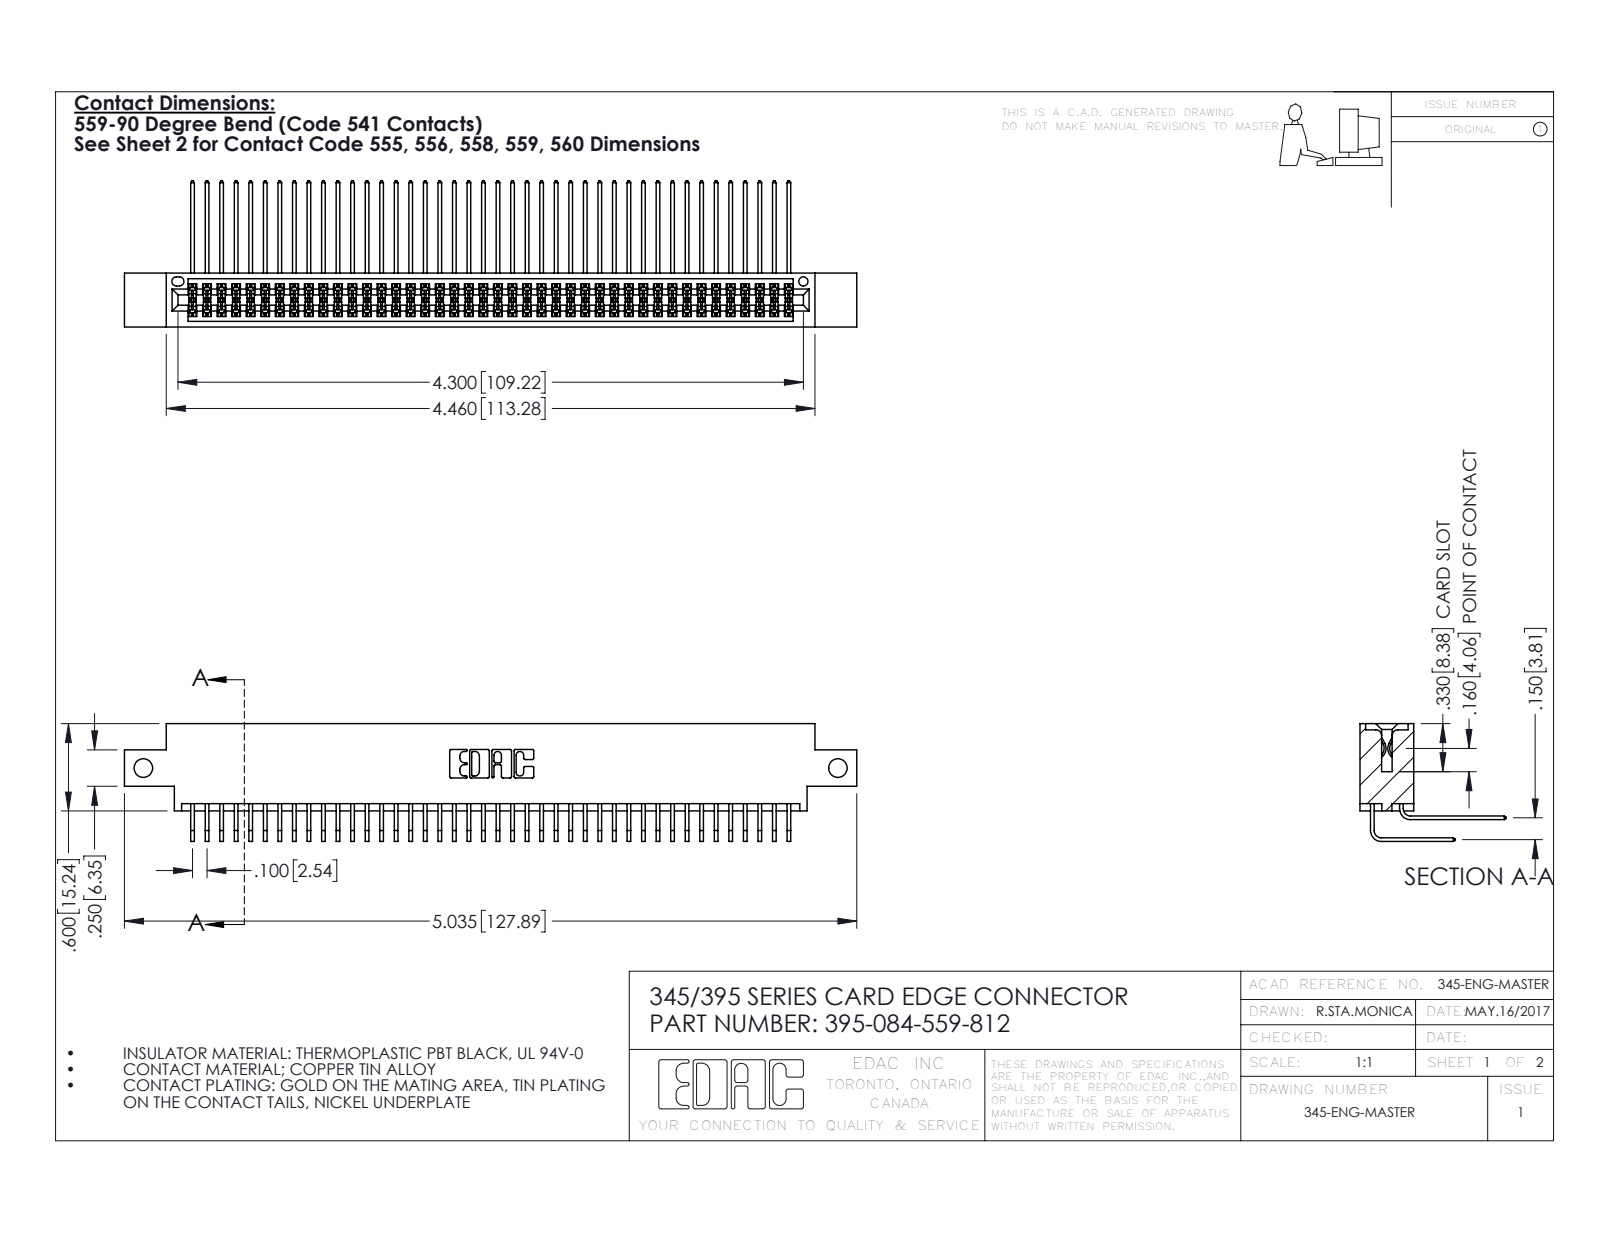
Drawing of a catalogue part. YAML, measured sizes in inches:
part_name: "395-084-559-812; 345 Part_0.170 Offset - Side Mount; 345-292-001_559 Tail - 2; 345-292-001_558 559 Tail - 1"
step_written_by: "SolidWorks 2016 (CONFIG_CONTROL_DESIGN)"
units: inches
bodies: {solids: 85, faces: 4498, planar: 3024, cylindrical: 1474, other: 0}
overall_size: [5.035, 1.005, 0.809]
volume: 0.775
surface_area: 32.66
round_holes:
  - {diameter: 0.128, count: 2}
  - {diameter: 0.064, count: 1}
partial_cylinders:
  - {radius: 0.006, count: 126}
  - {radius: 0.01, count: 22}
  - {radius: 0.007, count: 6}
  - {radius: 0.031, count: 6}
  - {radius: 0.026, count: 3}
  - {radius: 0.014, count: 2}
  - {radius: 0.019, count: 2}
  - {radius: 0.022, count: 2}
face_to_face_distances: [0.072, 0.298, 0.37, 0.2, 0.098, 0.272, 0.025, 0.225, 0.175, 0.15]
hole_center_spacings: [4.775]
